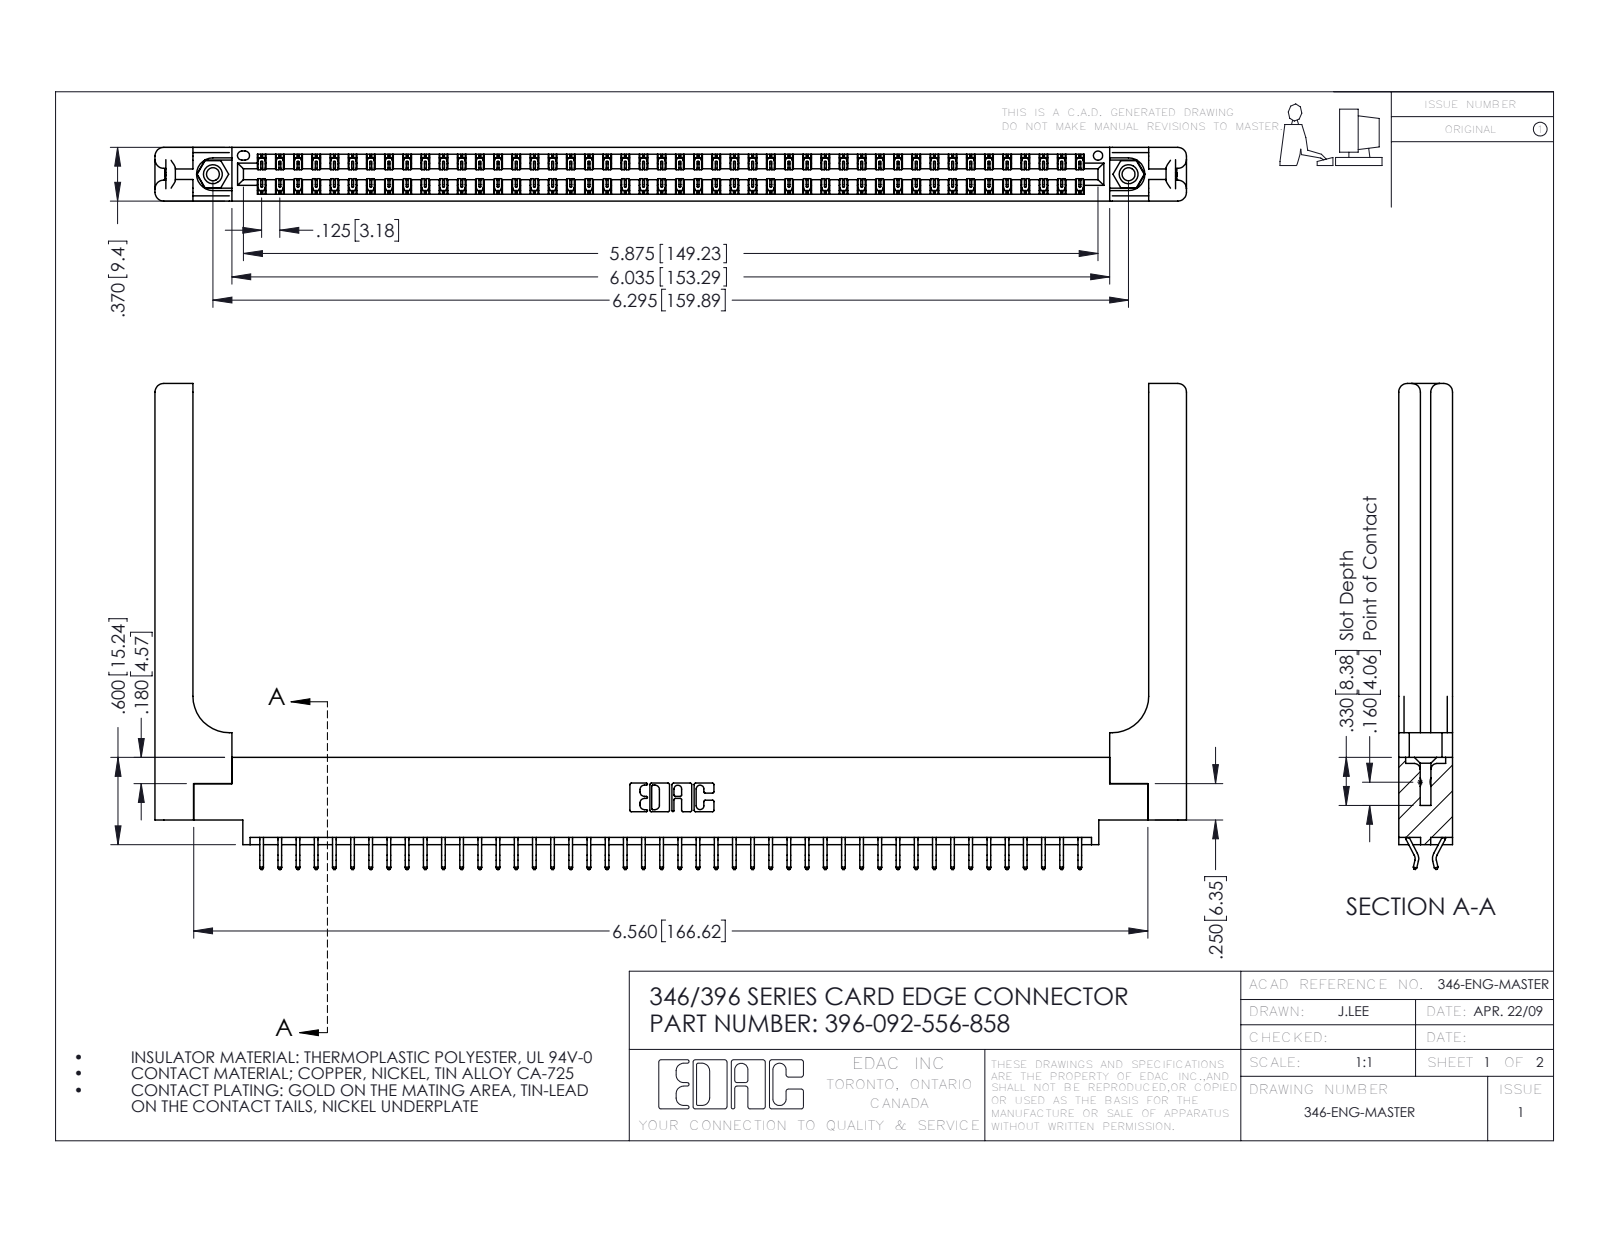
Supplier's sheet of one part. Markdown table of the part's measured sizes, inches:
| quantity | value |
| --- | --- |
| part name | 346 Part_0.170 Offset - 0.156 Dia-TH; 345-250-001_345-250-001-102; 345-292-001_556 Tail; 346-220-058_345-220-058 (+1 more) |
| STEP written by | SolidWorks 2016 (CONFIG_CONTROL_DESIGN) |
| units | inches |
| bodies | 97 solids, 5718 faces (3816 planar, 1842 cylindrical, 60 other) |
| overall size | 7.091 × 3.34 × 0.37 |
| volume | 1.521 in³ |
| surface area | 45.1 in² |
| round holes (diameter × count) | 0.089 × 2, 0.125 × 2, 0.156 × 2, 0.064 × 1 |
| round bosses / shafts (diameter × count) | 0.155 × 2 |
| partial cylindrical surfaces (radius × count) | 0.006 × 138, 0.01 × 22, 0.06 × 16, 0.007 × 6, 0.031 × 6, 0.026 × 3, 0.01 × 2, 0.014 × 2 |
| main face-to-face distances | 0.37, 0.048, 0.322, 0.072, 0.148, 0.15, 0.25, 0.025, 0.298, 0.275 |
| hole center spacings | 0.246, 6.086, 6.295 |
